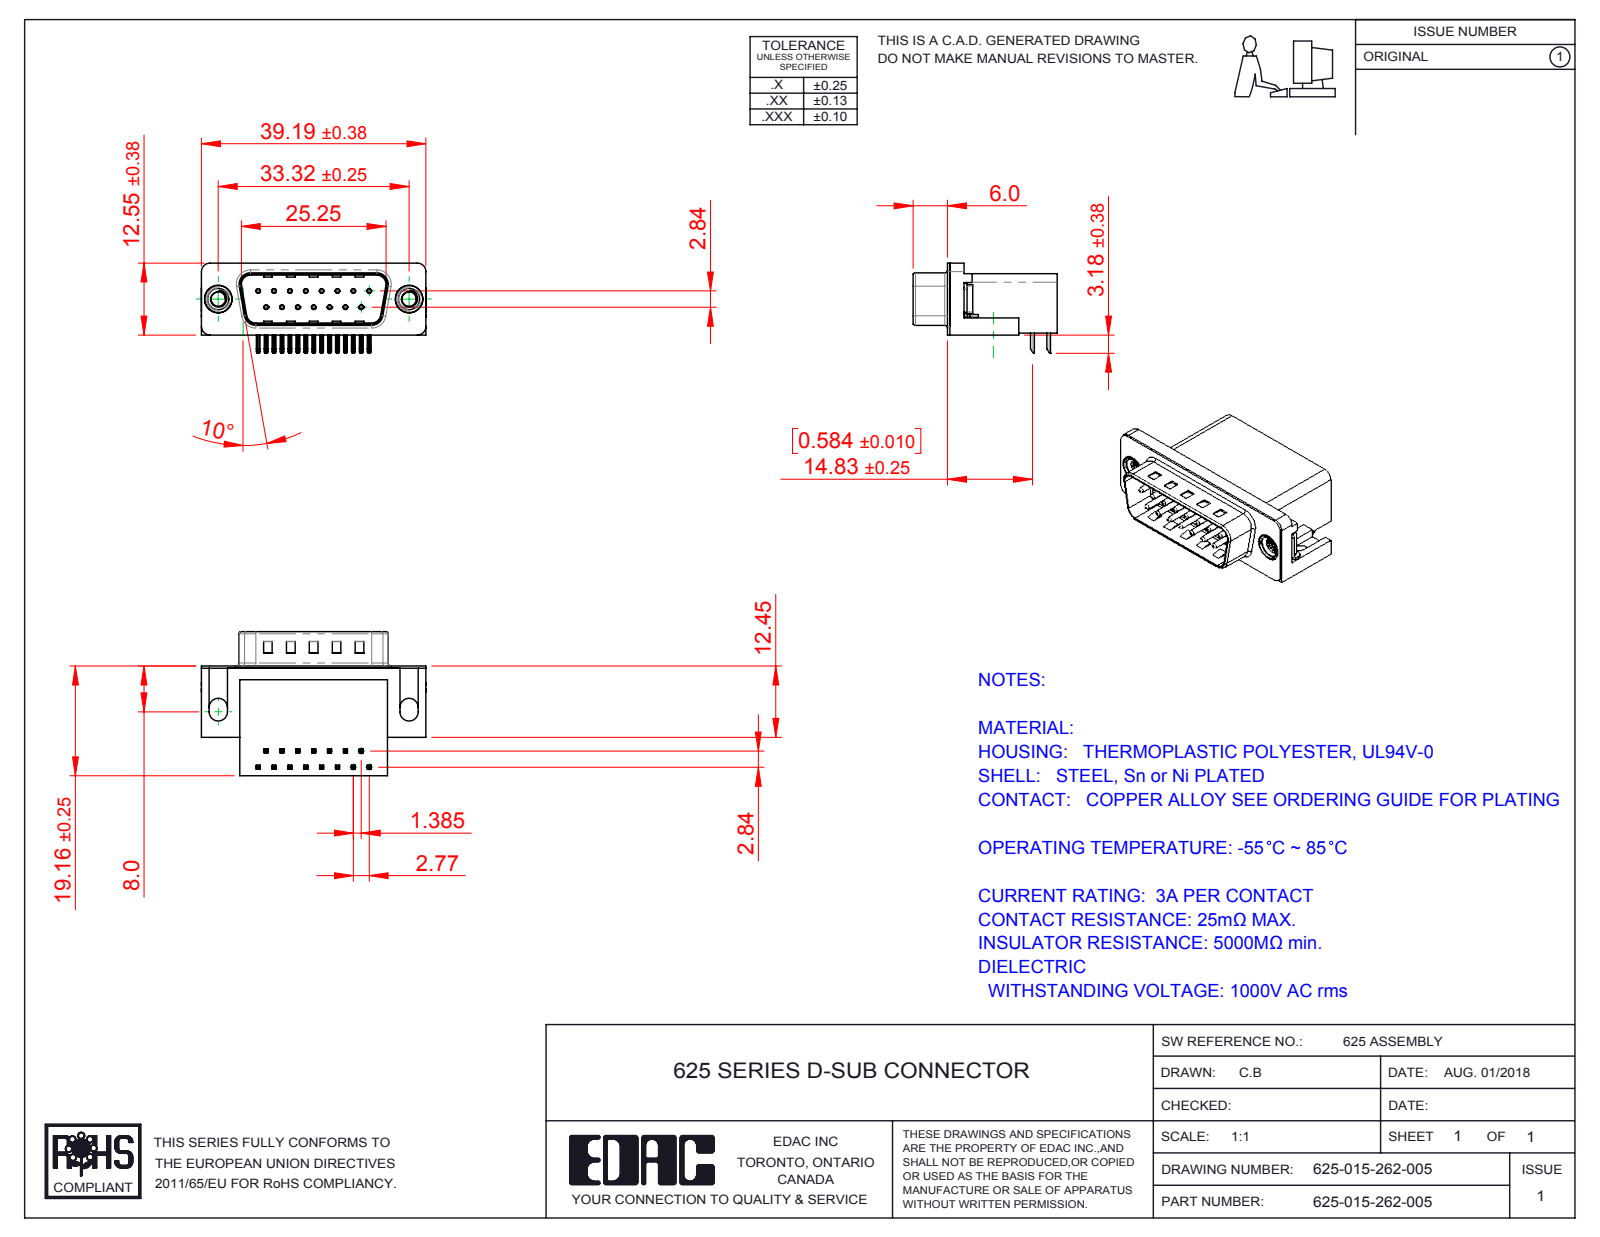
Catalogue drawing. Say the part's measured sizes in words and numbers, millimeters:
The part is named "625 Contact Bottom; 625-015-262-005; 625 Housing_15 Socket; 625 M3 Threaded Rivet (+3 more)". Its 3-D file was written by "SolidWorks 2016 (CONFIG_CONTROL_DESIGN)". It is 21 solids with 1477 faces: 895 planar, 447 cylindrical and 135 other. Overall it measures 39.22 by 25.16 by 15.73 millimeters. Its volume is 6 210 cubic millimeters and its surface area 6 294 square millimeters. Round holes: 15 of diameter 0.35, 15 of diameter 0.8, 2 of diameter 2.5, 2 of diameter 4, 2 of diameter 4.8, 2 of diameter 5. Round bosses or shafts: 15 of diameter 0.75, 2 of diameter 4.9, 2 of diameter 4.75, 2 of diameter 3.9. Partial cylindrical surfaces (rounded edges, fillets, slot ends): 68 of radius 0.25, 30 of radius 0.12, 16 of radius 1, 9 of radius 0.5, 8 of radius 1.6, 6 of radius 1.5, 4 of radius 0.9, 4 of radius 2. The main face-to-face distances are 0.4, 10.35, 18.76, 2.1, 10.46, 19.16, 1.7, 10.86, 8.76, 16.26. The hole center spacings are 3.16, 2.77, 5.54, 8.31, 11.08, 5.03, 5.04, 7.48.
